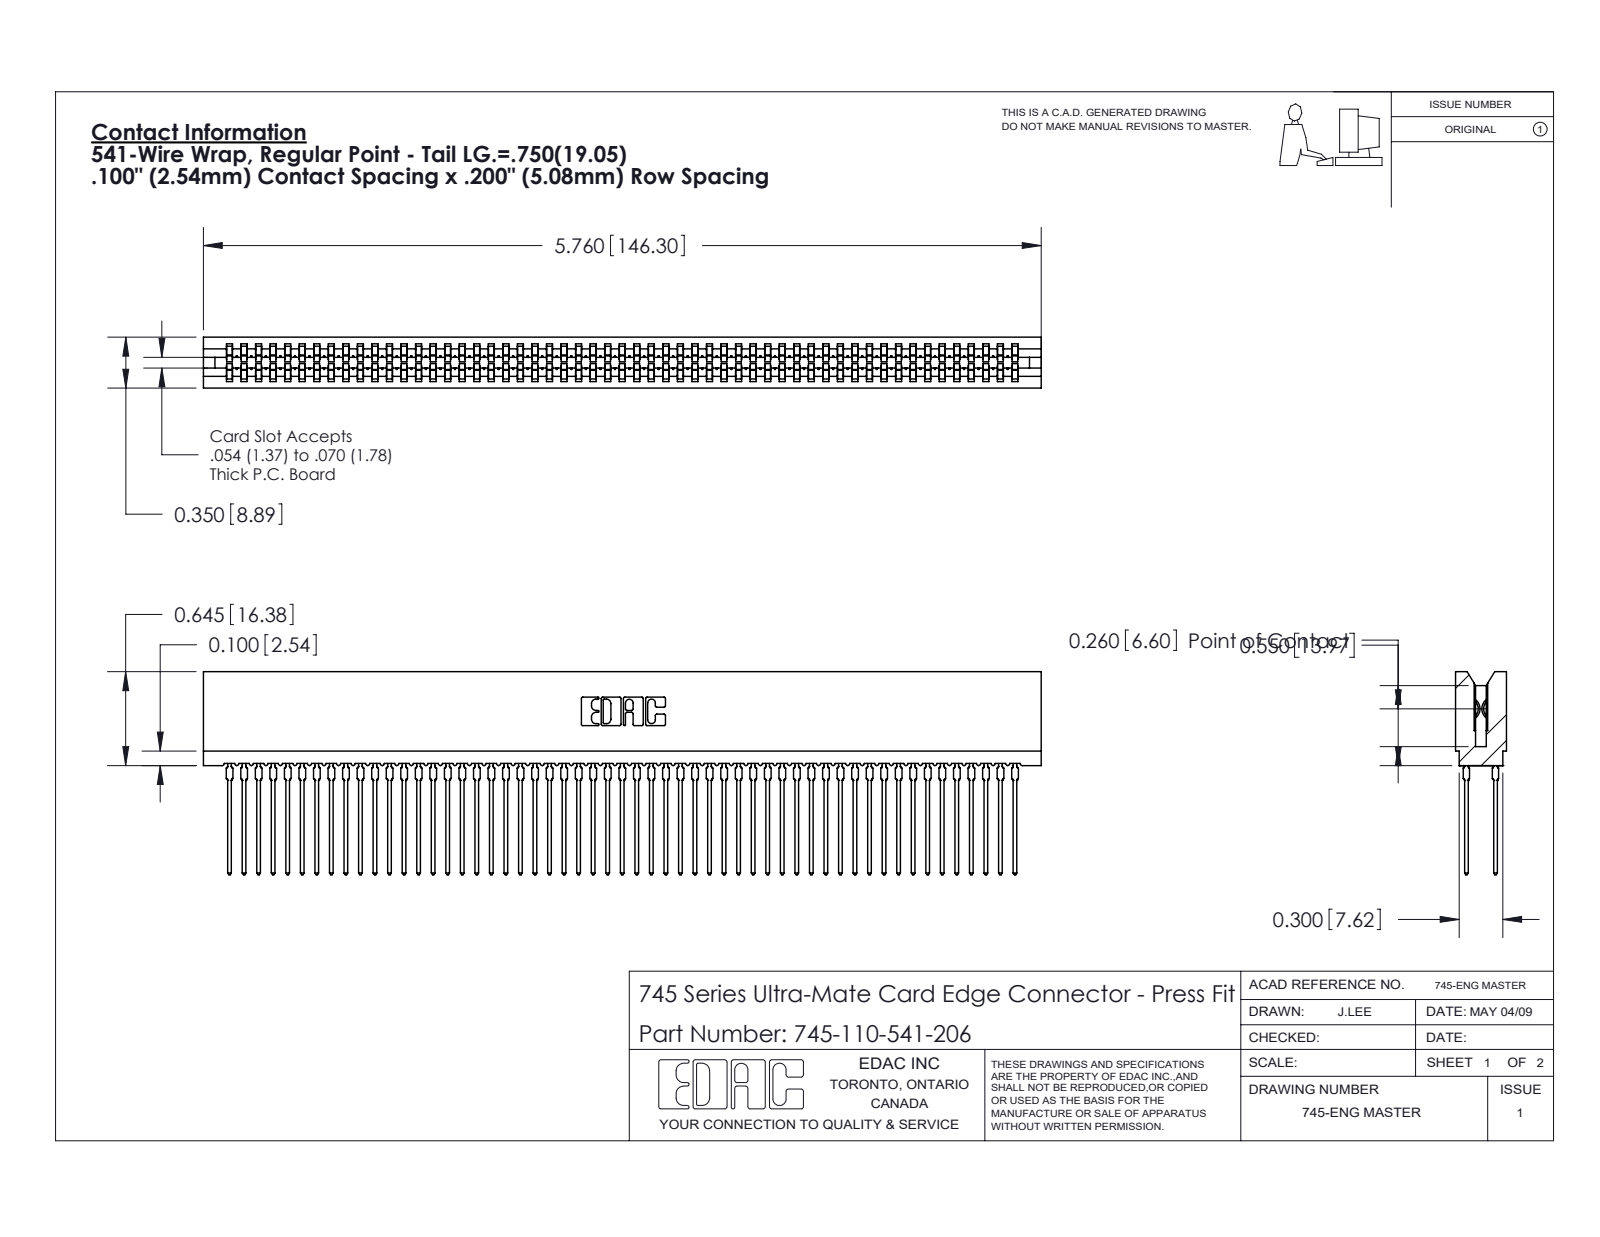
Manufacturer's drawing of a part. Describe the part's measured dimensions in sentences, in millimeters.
The part is named "745-292-001_541; 745-110-541-206; 745 Part_Insulator Option - 06". Its 3-D file was written by "SolidWorks 2020 (CONFIG_CONTROL_DESIGN)". It is 111 solids with 9941 faces: 5116 planar, 1965 cylindrical and 2860 other. Overall it measures 146.3 by 35.5 by 8.9 millimeters. Its volume is 13 600 cubic millimeters and its surface area 30 190 square millimeters. Partial cylindrical surfaces (rounded edges, fillets, slot ends): 220 of radius 0.5, 110 of radius 0.4, 22 of radius 0.3, 8 of radius 0.1, 8 of radius 0.3, 6 of radius 0.2, 6 of radius 0.8, 3 of radius 0.7. The main face-to-face distances are 1.6, 7.3, 5.1, 8.9, 2.2, 6.7, 0.6, 1.1, 7.7, 0.5.
